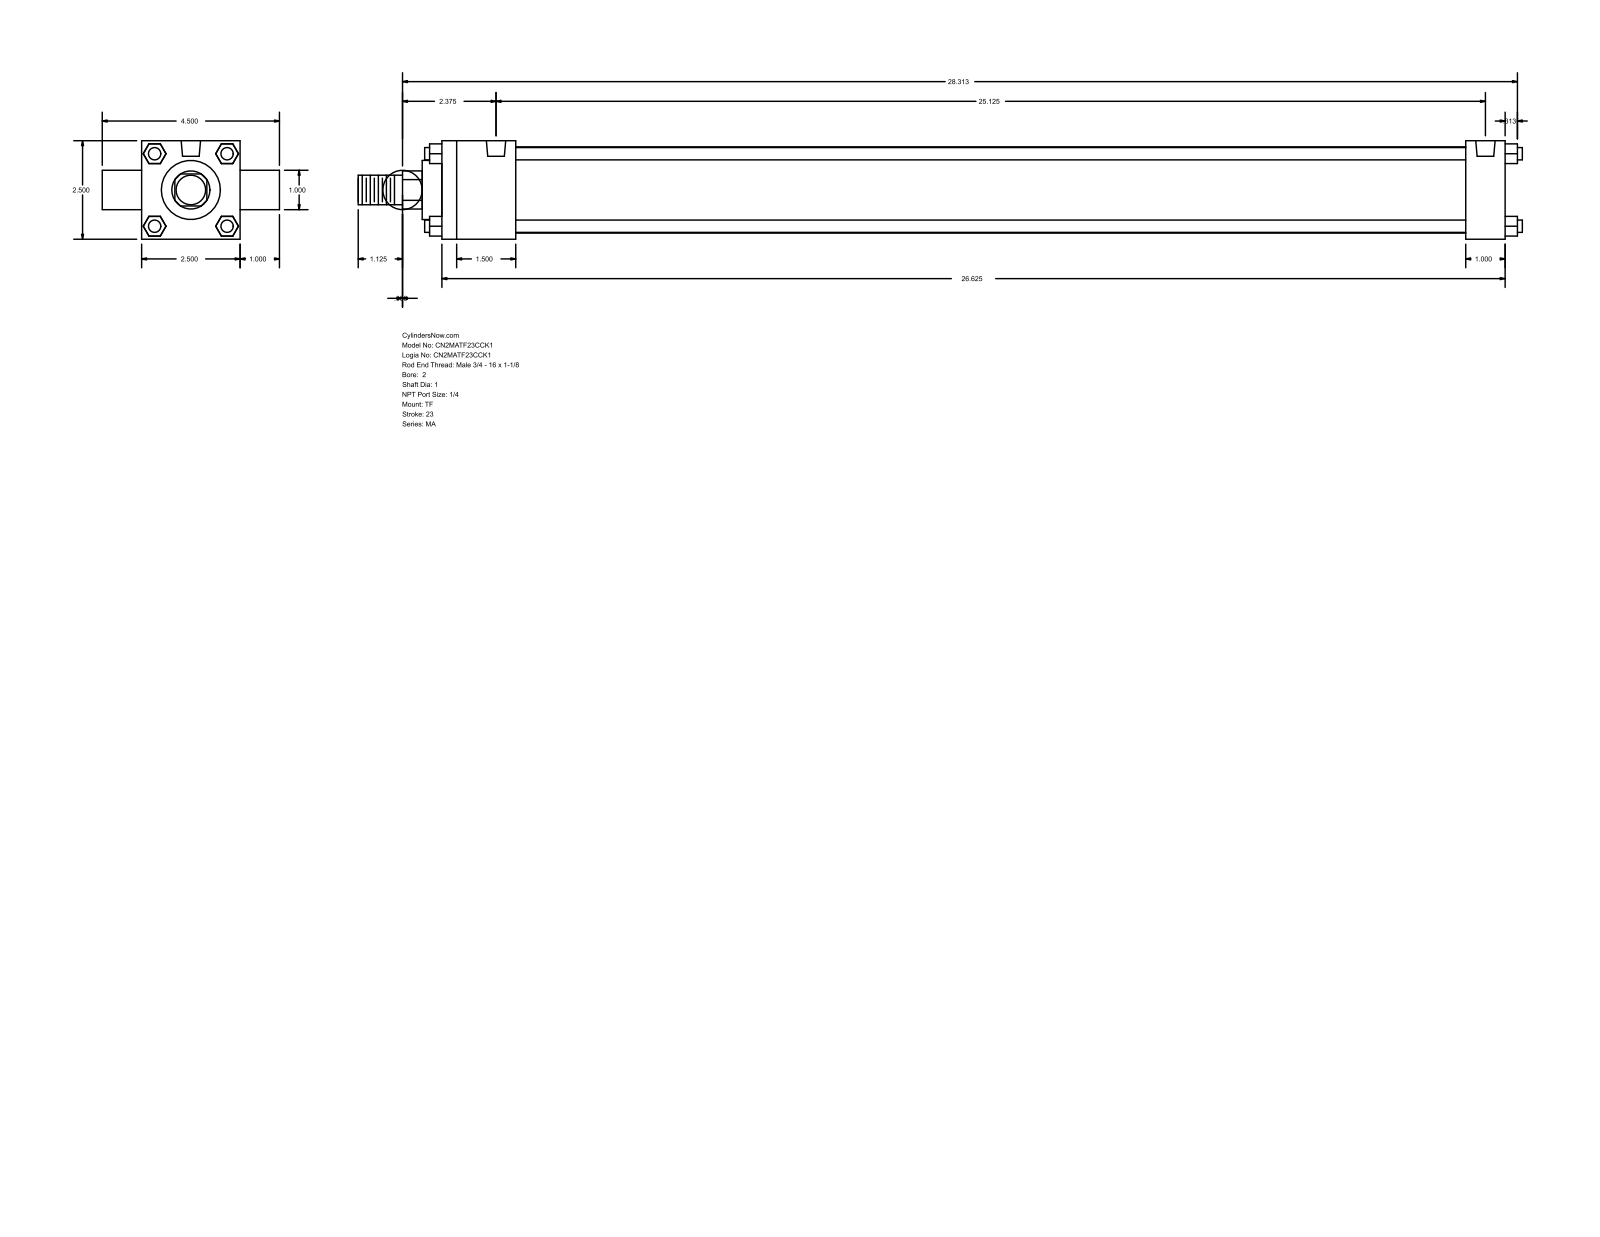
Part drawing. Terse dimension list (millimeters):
name: MA_TF__0200_1
written by: GSSL Pune (CONFIG_CONTROL_DESIGN)
unit: mm
bodies: 0 solids, 120 faces (92 planar, 28 cylindrical, 0 other)
size: 750.89 × 114.3 × 63.5
holes: 3× ⌀7.94, 2× ⌀12.49
bosses: 4× ⌀7.94, 2× ⌀25.4, 1× ⌀55.63, 1× ⌀38.1, 1× ⌀19.05
rounds: 1× R12.29
face distances: 63.5, 25.4, 685.8, 12.7, 47.63, 660.4, 612.77, 638.17, 88.9, 40.47
hole spacings: 638.17
